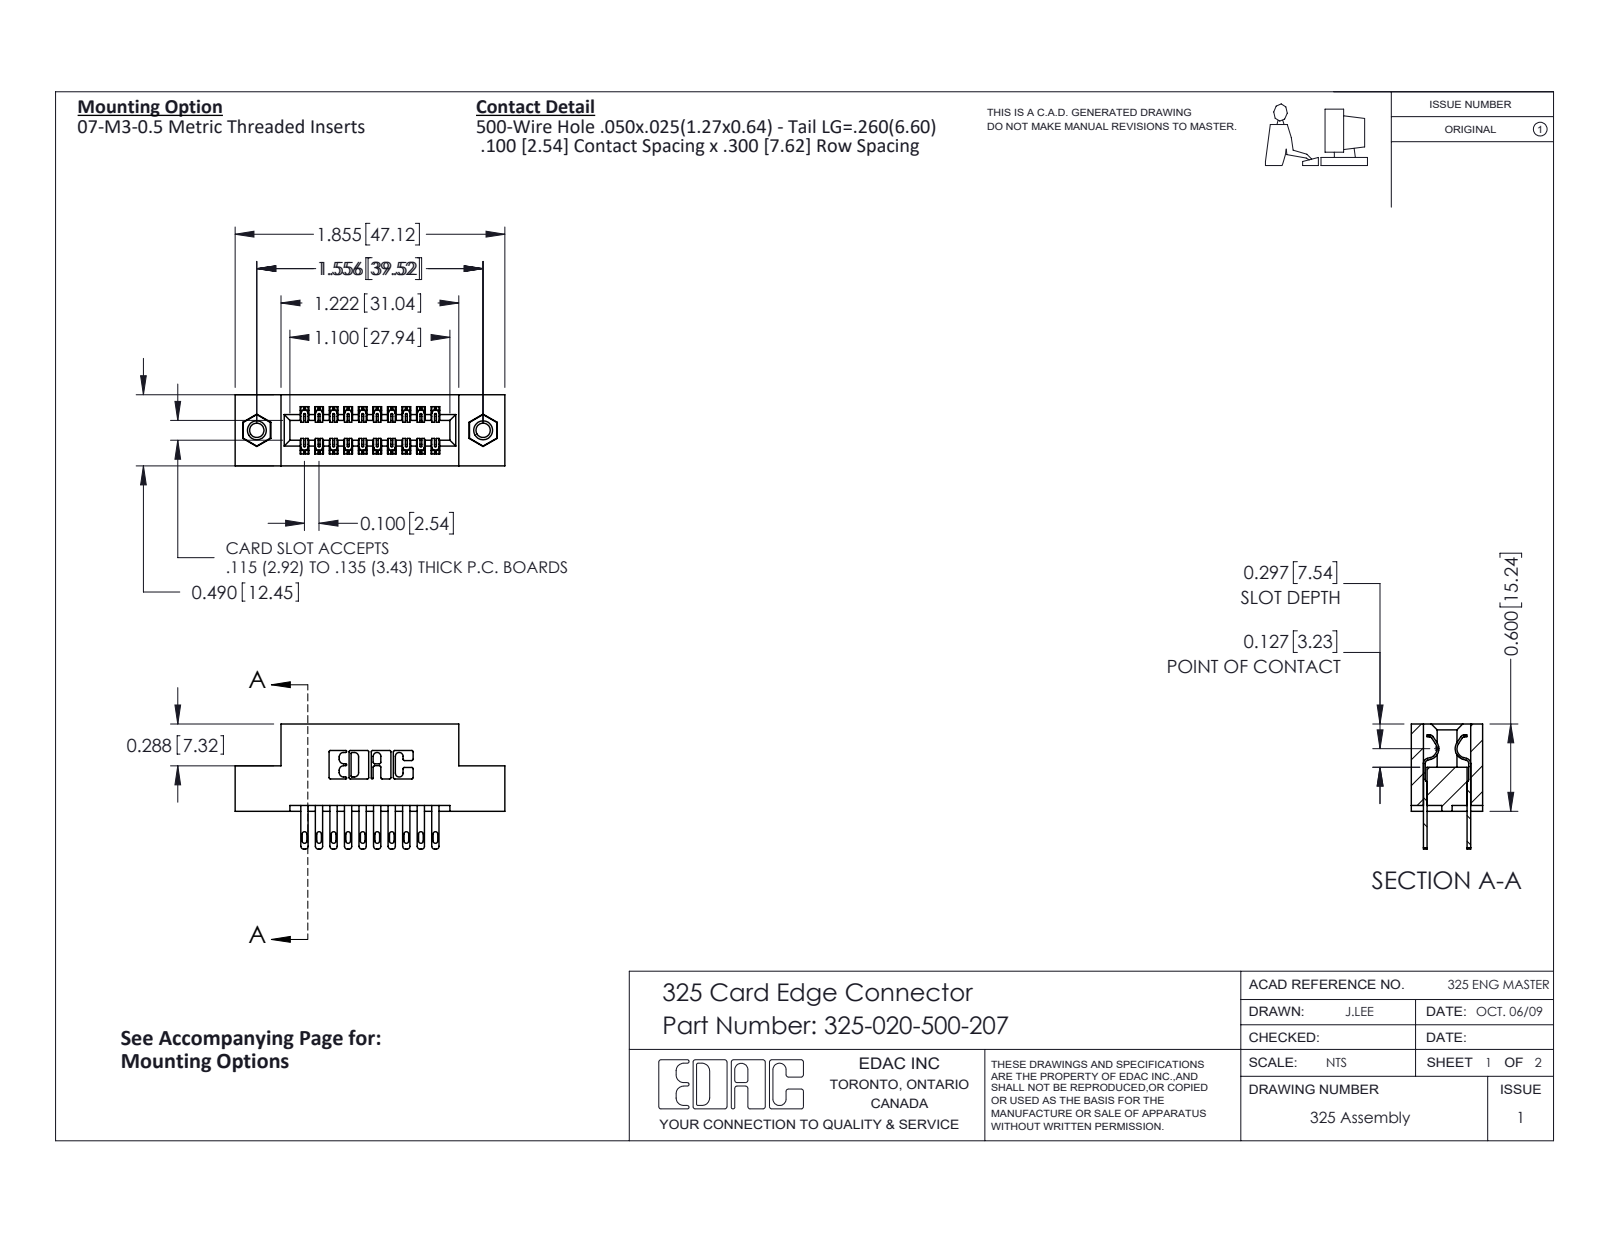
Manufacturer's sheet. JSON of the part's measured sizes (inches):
{"part_name": "325 Part_TI; 325-292-001_325-293-100; 325-020-500-207; 345-250-001_345-250-005-103", "step_written_by": "SolidWorks 2016 (CONFIG_CONTROL_DESIGN)", "units": "inches", "bodies": {"solids": 23, "faces": 1134, "planar": 702, "cylindrical": 416, "other": 16}, "overall_size": [1.855, 0.86, 0.49], "volume_in3": 0.357, "surface_area_in2": 10.15, "round_holes": [[0.098, 2], [0.125, 2], [0.16, 2]], "round_bosses_or_shafts": [[0.155, 2]], "partial_cylinders_radius": [[0.006, 30], [0.01, 22], [0.016, 20], [0.02, 20], [0.007, 6], [0.031, 6], [0.026, 3], [0.014, 2]], "face_to_face_distances": [0.3, 0.083, 0.407, 0.49, 0.04, 0.1, 0.2, 0.107, 0.383, 0.025], "hole_center_spacings": [1.556]}
